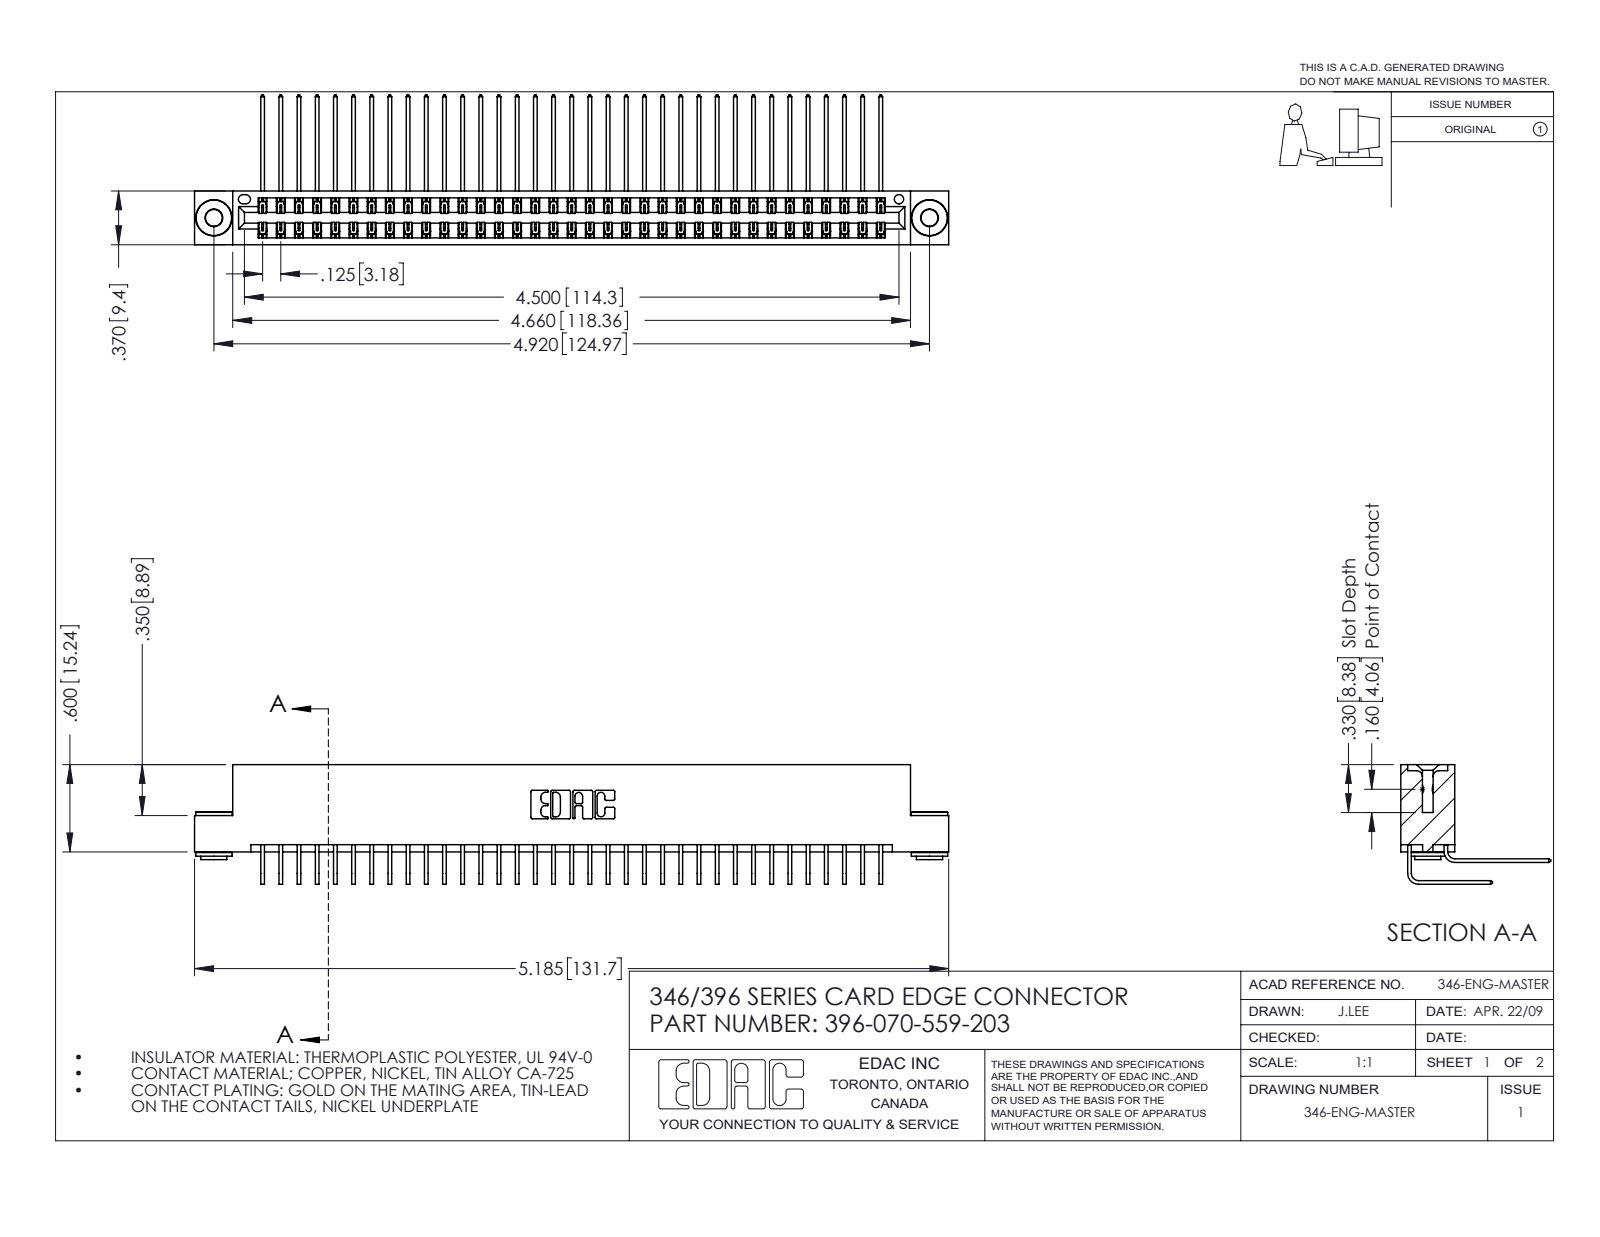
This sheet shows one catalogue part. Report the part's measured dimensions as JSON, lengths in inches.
{"part_name": "345-292-001_559 Tail - 2; 396-070-559-203; 345-250-002_345-250-002-102; 346 Part_Flush Mounting Lugs - 0.156 Dia-TH (+1 more)", "step_written_by": "SolidWorks 2016 (CONFIG_CONTROL_DESIGN)", "units": "inches", "bodies": {"solids": 73, "faces": 3940, "planar": 2676, "cylindrical": 1256, "other": 8}, "overall_size": [5.185, 1.03, 0.823], "volume_in3": 0.806, "surface_area_in2": 31.31, "round_holes": [[0.116, 2], [0.156, 2], [0.064, 1]], "round_bosses_or_shafts": [[0.25, 2], [0.18, 2], [0.136, 2]], "partial_cylinders_radius": [[0.006, 105], [0.01, 22], [0.007, 6], [0.031, 6], [0.026, 3], [0.014, 2], [0.022, 2], [0.024, 2]], "face_to_face_distances": [0.048, 0.322, 0.025, 0.25, 0.37, 0.072, 0.298, 0.275, 0.148, 0.222], "hole_center_spacings": [0.246, 4.711, 4.92]}
